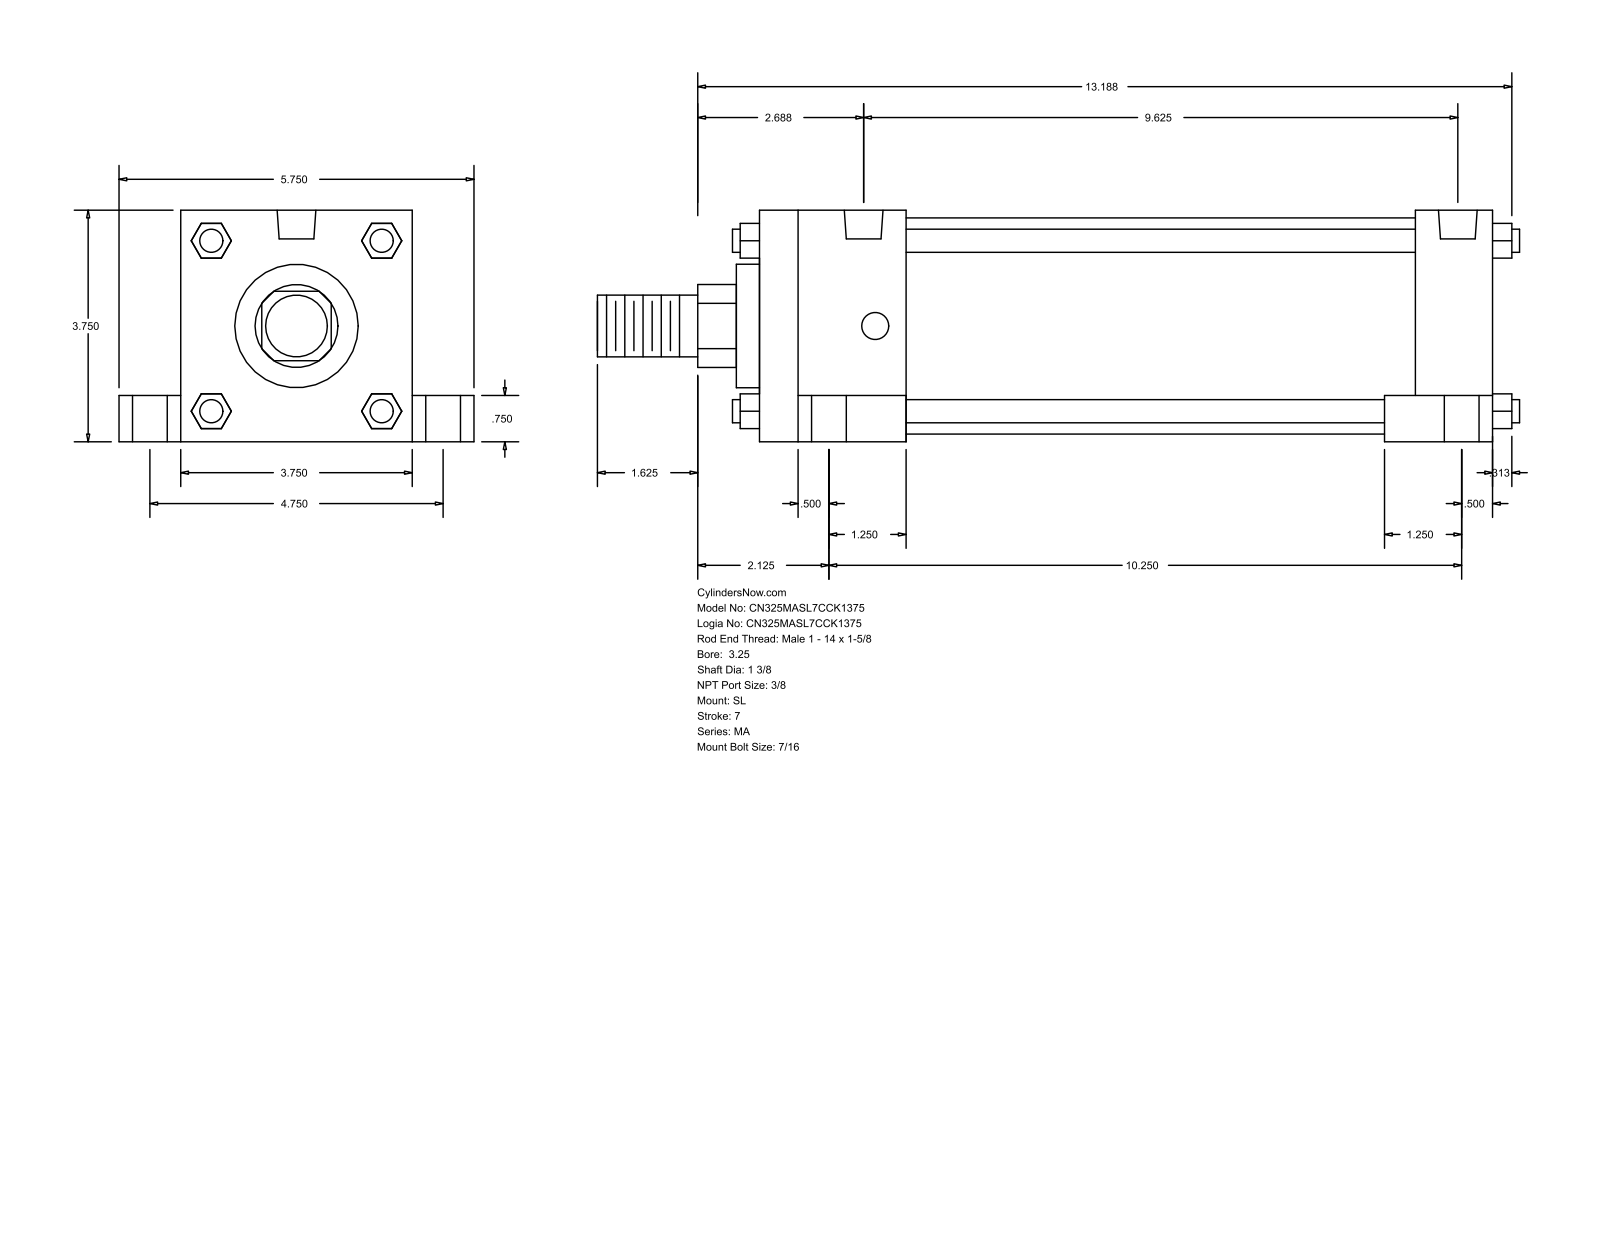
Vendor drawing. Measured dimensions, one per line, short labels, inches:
name: MA_SL__0325_1.375
written by: GSSL Pune (CONFIG_CONTROL_DESIGN)
unit: in
bodies: 0 solids, 148 faces (112 planar, 36 cylindrical, 0 other)
size: 14.937 × 5.75 × 3.75
holes: 4× ⌀0.437, 4× ⌀0.563, 4× ⌀0.813, 2× ⌀0.627
bosses: 4× ⌀0.375, 1× ⌀3.5, 1× ⌀2, 1× ⌀1.375, 1× ⌀1
rounds: 1× R0.672
face distances: 3.75, 11.875, 8.25, 1, 4.75, 10.625, 1.25, 2.375, 9.5, 0.75
hole spacings: 2.376, 2.388, 2.441, 2.491, 4.75, 9.25, 9.792, 9.974
